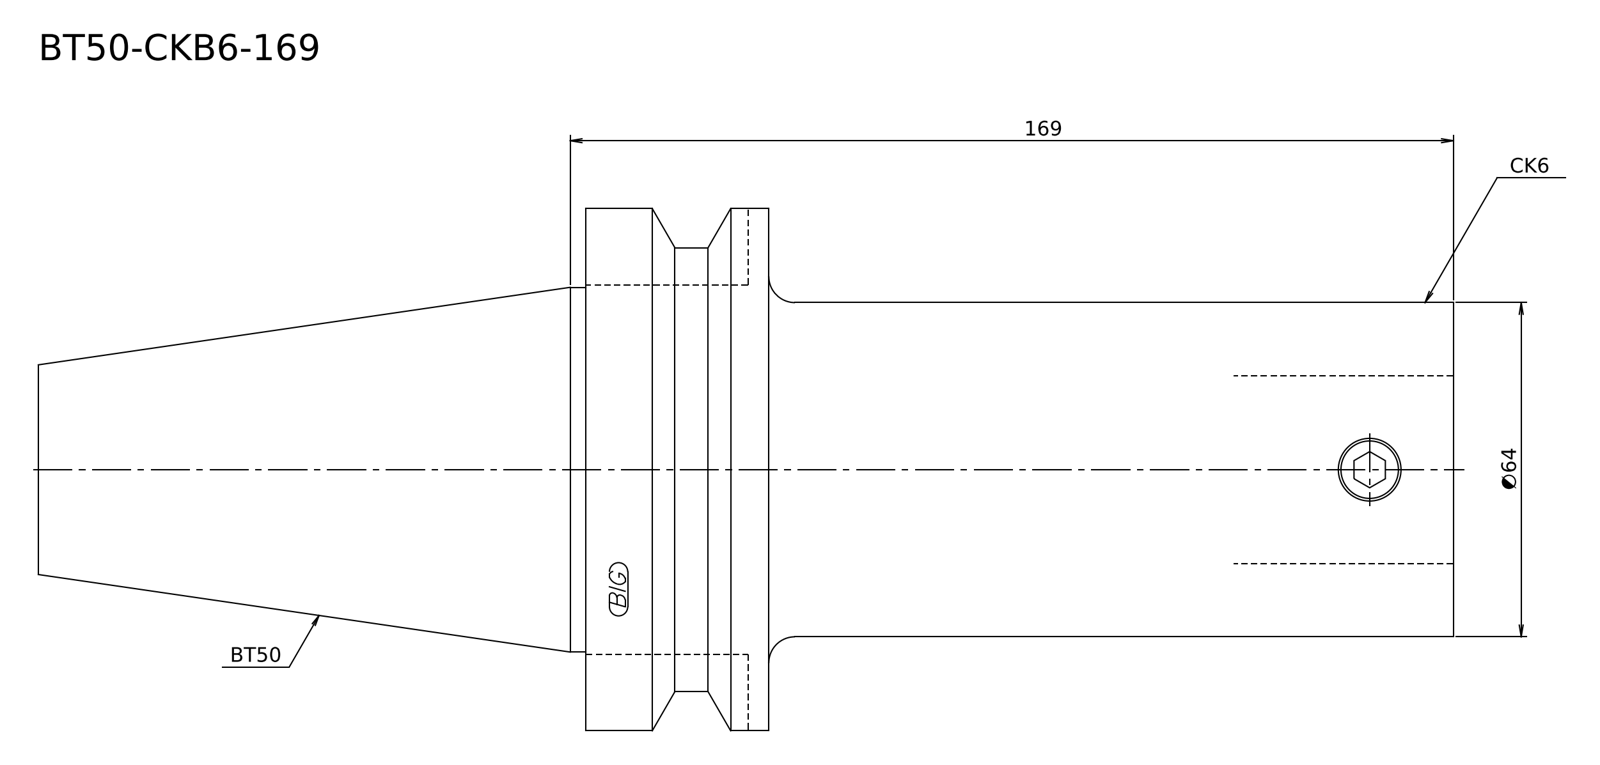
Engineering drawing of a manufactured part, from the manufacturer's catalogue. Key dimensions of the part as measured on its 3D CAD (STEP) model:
STEP written by: Kubotek KeyCreator V8.5.1 (14335) (CONFIG_CONTROL_DESIGN)
Units: millimetres
Bodies: 1 solid, 13 faces (4 planar, 5 cylindrical, 4 other)
Overall size (bounding box): 270.8 × 100 × 100
Volume: 934 715 mm³ · Surface area: 70 370 mm²
Round bosses / shafts (diameter × count): ⌀100 ×1, ⌀85 ×1, ⌀69.85 ×1, ⌀64 ×1
Main face-to-face distances: 35, 131, 166, 270.8, 139.8, 104.8
